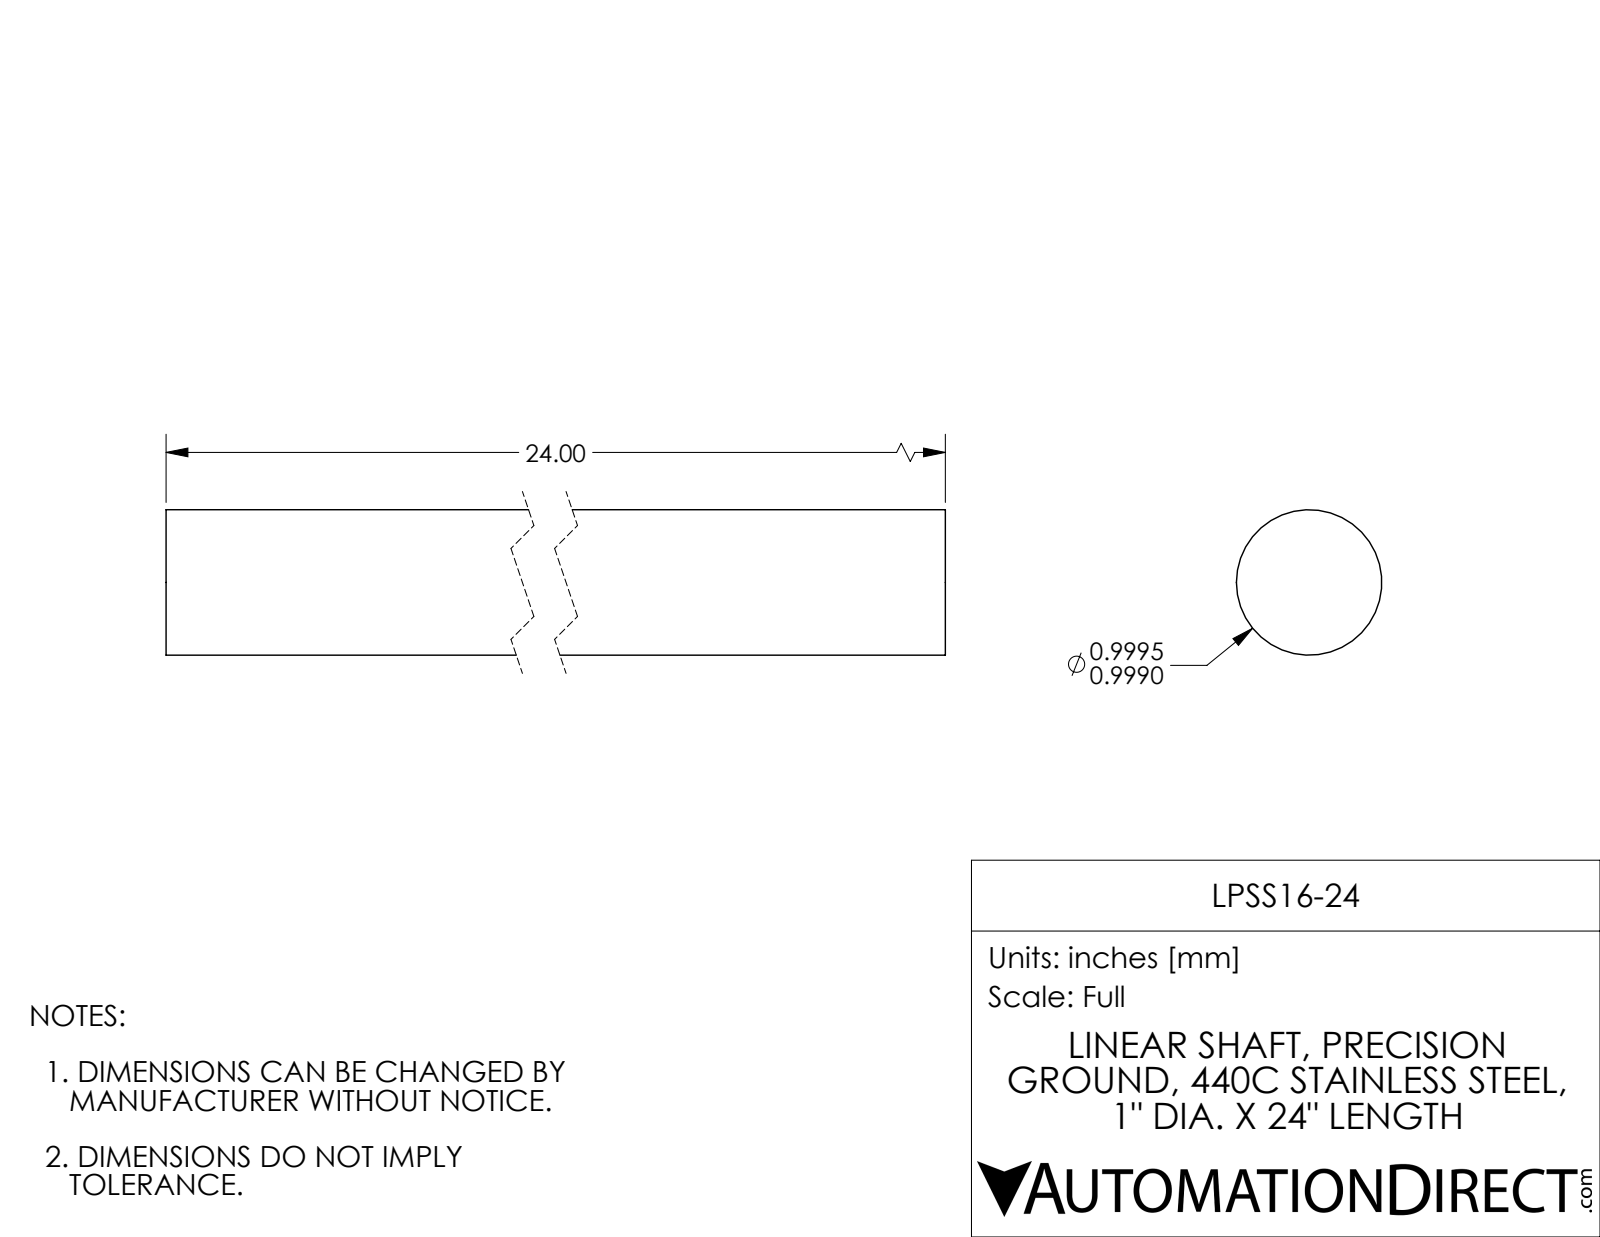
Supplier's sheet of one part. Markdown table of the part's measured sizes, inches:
| quantity | value |
| --- | --- |
| part name | LPSS16-24 |
| STEP written by | SolidWorks 2017 (AUTOMOTIVE_DESIGN) |
| units | inches |
| bodies | 1 solid, 4 faces (2 planar, 2 cylindrical, 0 other) |
| overall size | 24 × 0.999 × 0.999 |
| volume | 18.83 in³ |
| surface area | 76.93 in² |
| round bosses / shafts (diameter × count) | 1 × 1 |
| main face-to-face distances | 24 |
